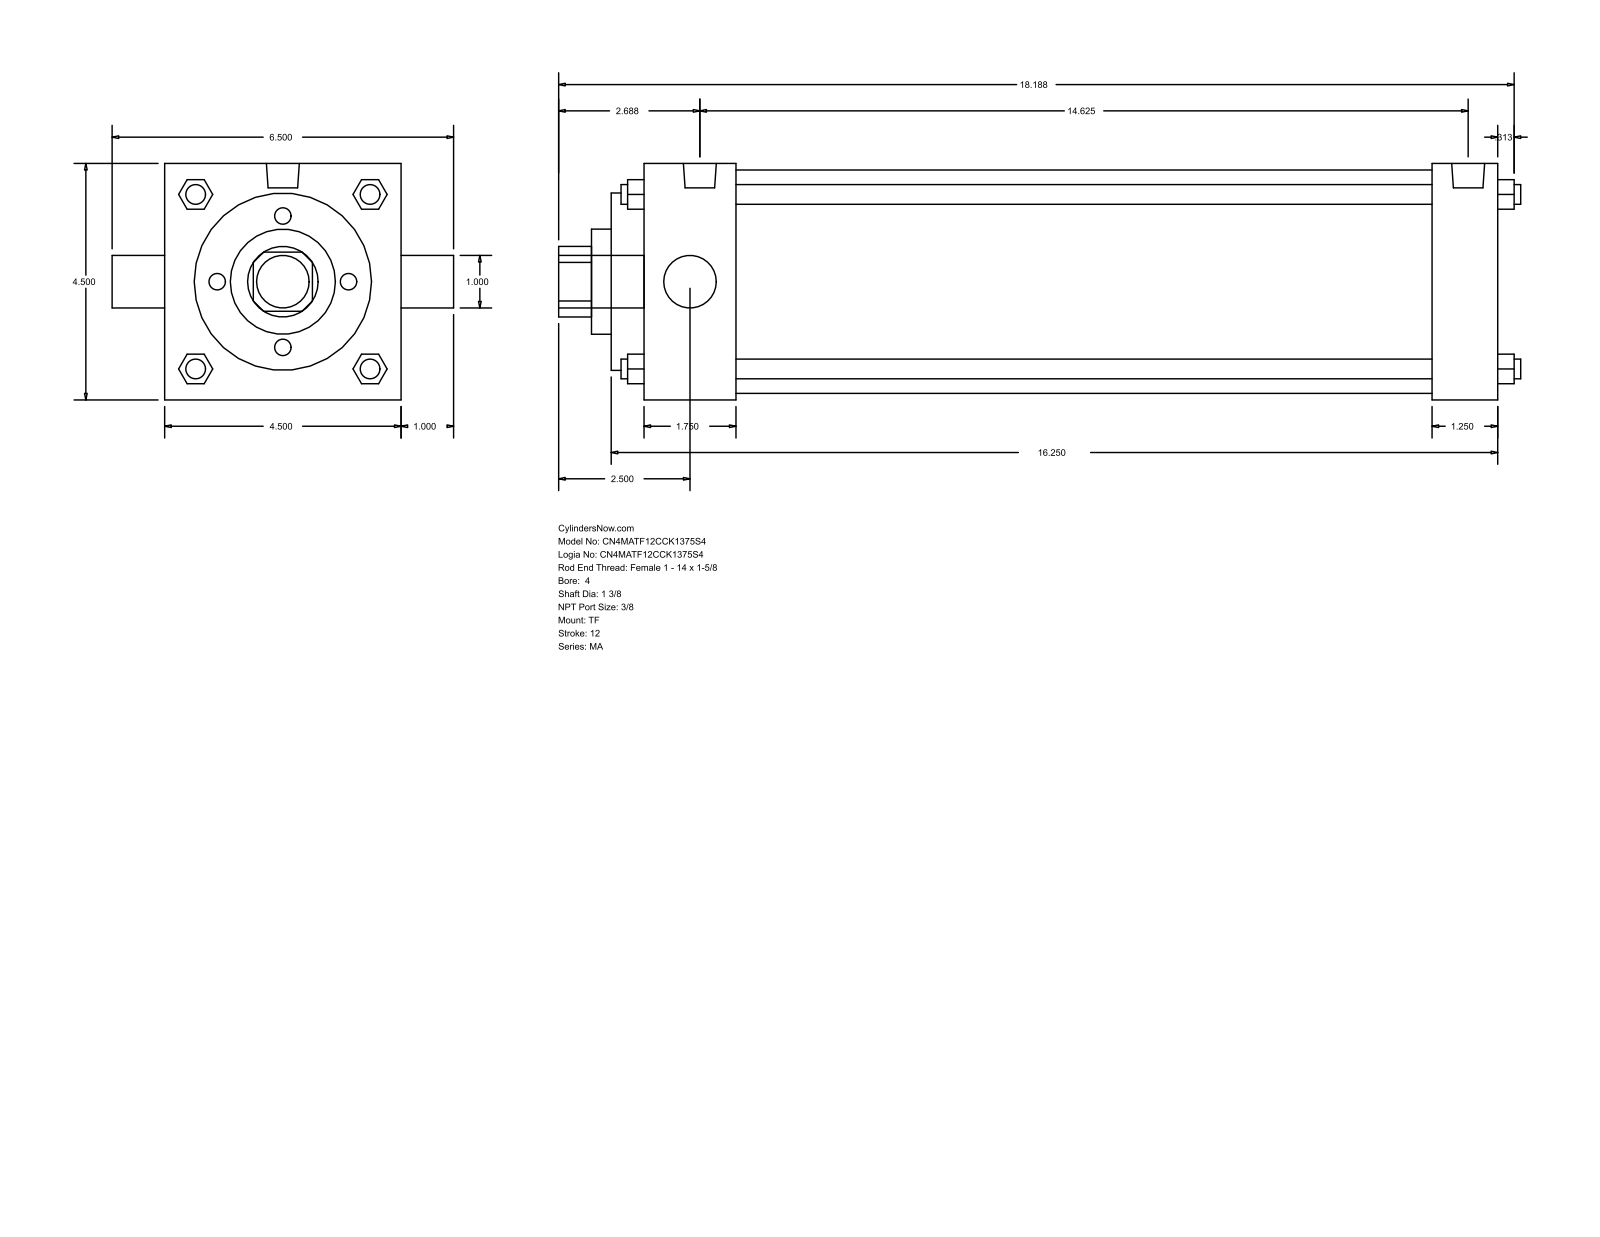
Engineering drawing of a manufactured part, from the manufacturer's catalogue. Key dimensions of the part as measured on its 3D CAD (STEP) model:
Part name (STEP PRODUCT): MA_TF__0400_1.375
STEP written by: GSSL Pune (CONFIG_CONTROL_DESIGN)
Units: millimetres
Bodies: 0 solids, 122 faces (93 planar, 29 cylindrical, 0 other)
Overall size (bounding box): 465.14 × 165.1 × 114.3
Round holes (diameter × count): ⌀25.4 ×1, ⌀34.92 ×1, ⌀50.8 ×1, ⌀85.72 ×1, ⌀107.95 ×1
Round bosses / shafts (diameter × count): ⌀9.53 ×4, ⌀11.11 ×3, ⌀15.93 ×2, ⌀25.4 ×1
Partial cylindrical surfaces — rounded edges, fillets, slot ends (radius × count): R17.06 ×1
Main face-to-face distances: 114.3, 412.75, 428.62, 15.87, 396.87, 381, 31.75, 60.32, 44.45, 336.55
